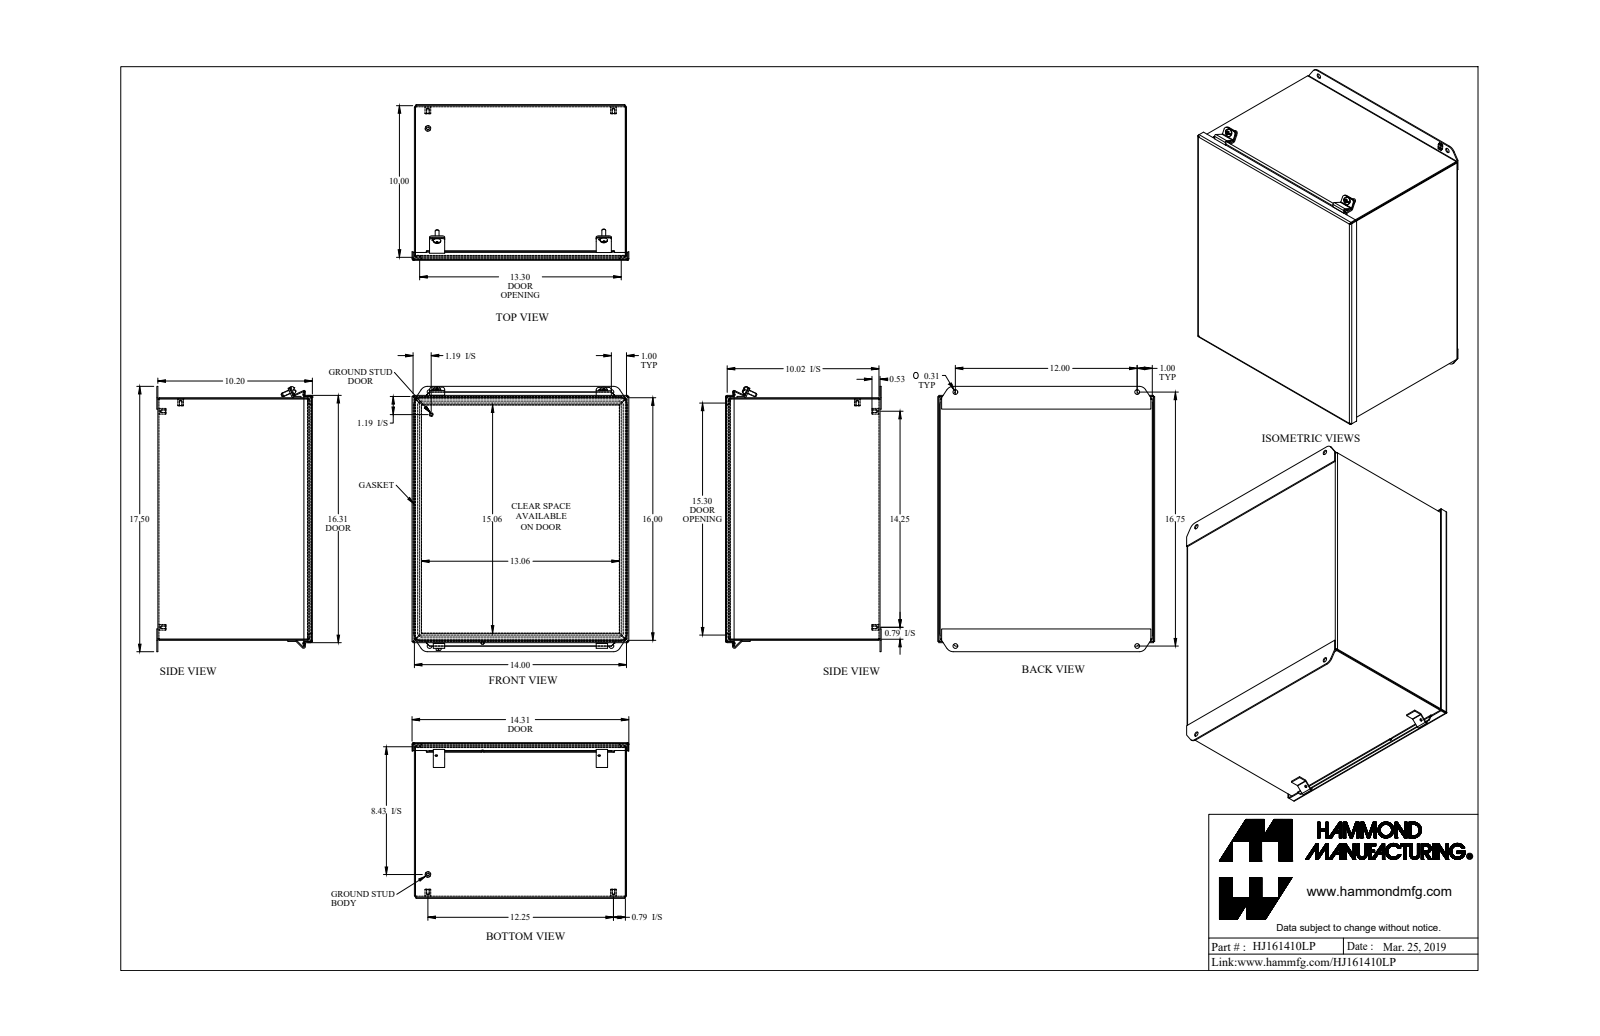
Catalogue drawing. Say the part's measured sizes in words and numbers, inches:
The part is named "HJ161410LP". Its 3-D file was written by "SolidWorks 2018 (AUTOMOTIVE_DESIGN)". It is 19 solids with 627 faces: 341 planar, 160 cylindrical and 126 other. Overall it measures 17.5 by 14.312 by 10.269 inches. Its volume is 88.16 cubic inches and its surface area 2 444 square inches. Round holes: 5 of diameter 0.156, 4 of diameter 0.313, 2 of diameter 0.156, 2 of diameter 0.213. Round bosses or shafts: 5 of diameter 0.375, 3 of diameter 0.25, 2 of diameter 0.48, 1 of diameter 0.188. Partial cylindrical surfaces (rounded edges, fillets, slot ends): 16 of radius 0.036, 16 of radius 0.108, 16 of radius 0.25, 4 of radius 0.01, 4 of radius 0.029, 4 of radius 0.086, 4 of radius 0.141, 4 of radius 0.188. The main face-to-face distances are 0.072, 10.125, 13.928, 15.928, 10.197, 10.053, 13.856, 14, 16, 15.856. The hole center spacings are 12, 12.25, 14.25, 16.75, 18.792, 20.605, 1.239, 1.243.
